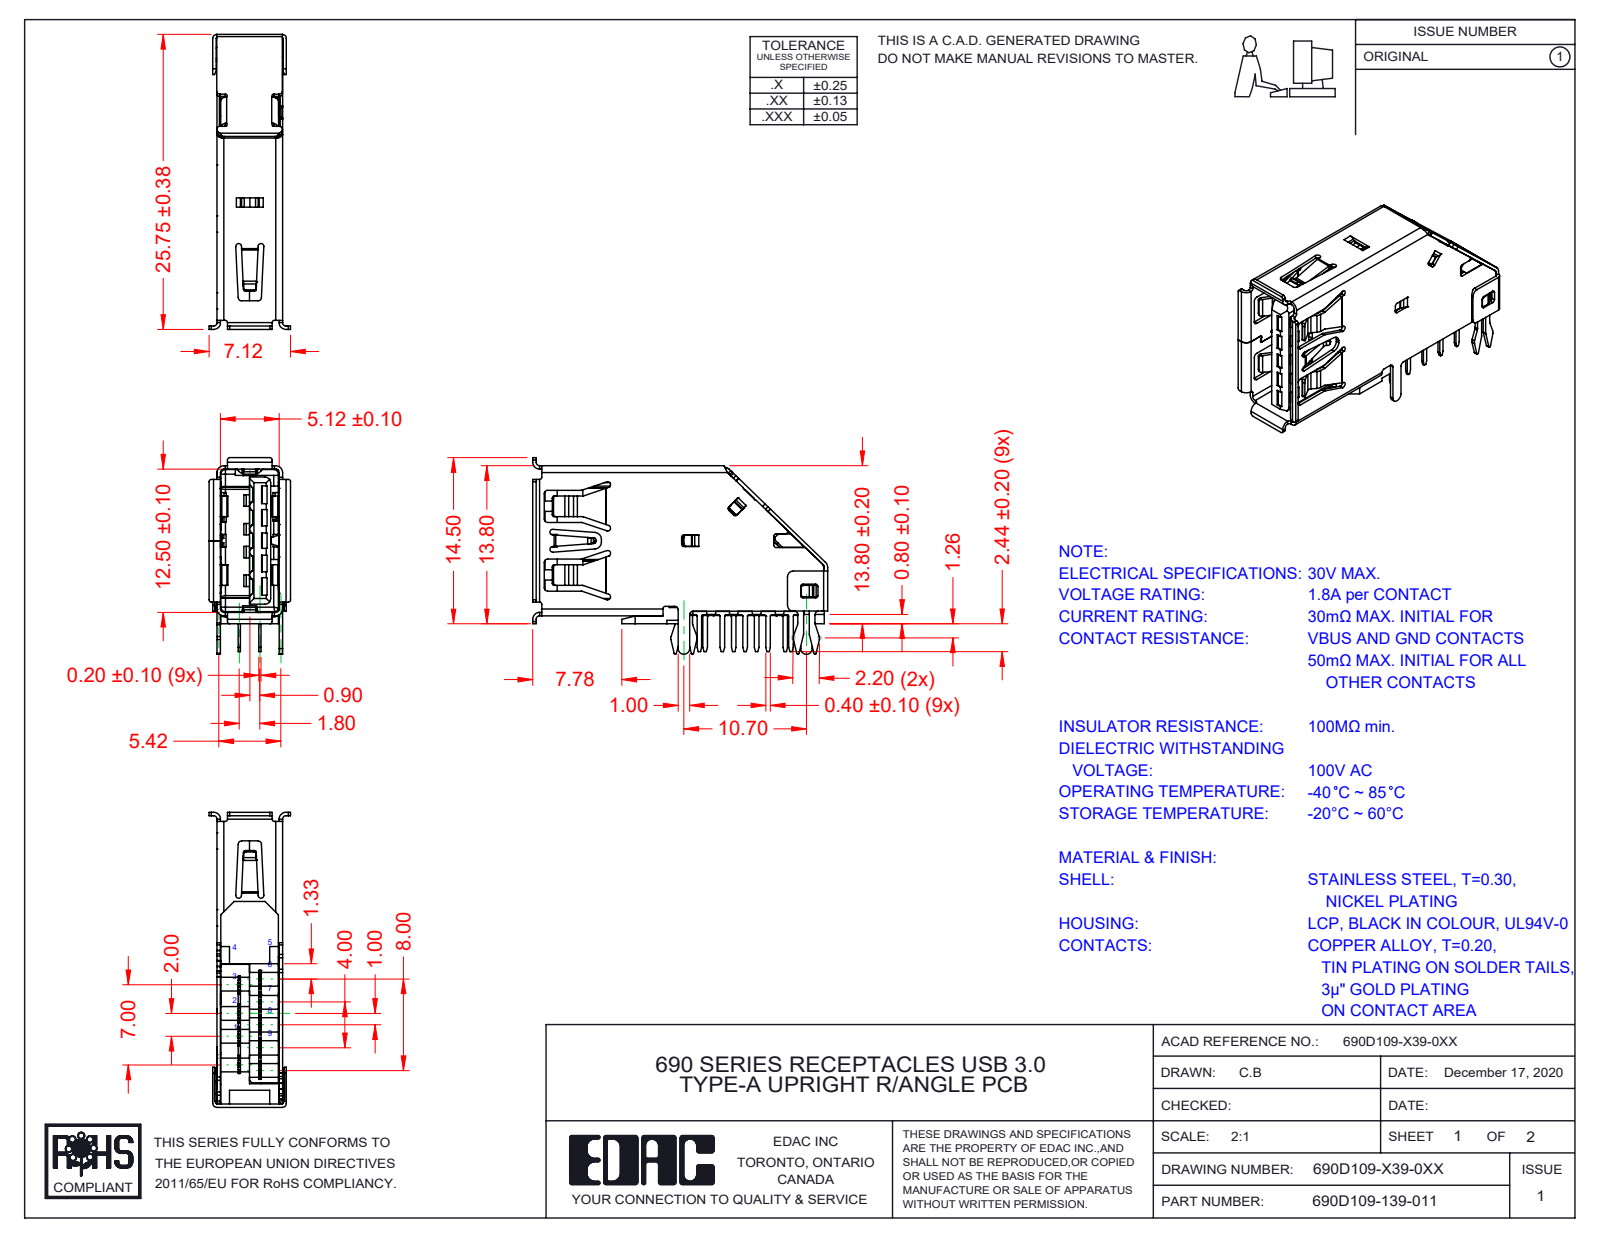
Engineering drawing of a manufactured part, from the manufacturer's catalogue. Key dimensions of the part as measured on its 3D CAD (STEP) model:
Part name (STEP PRODUCT): Contact 2.0 1 690D109-X39-0XX; Contact 3.0 6 690D109-X39-0XX; Contact 2.0 3 690D109-X39-0XX; Shell 2 690D109-X39-0XX (+8 more)
STEP written by: SolidWorks 2020 (AUTOMOTIVE_DESIGN)
Units: millimetres
Bodies: 13 solids, 2780 faces (1938 planar, 770 cylindrical, 72 other)
Overall size (bounding box): 25.75 × 17.16 × 7.12
Volume: 1 030 mm³ · Surface area: 4 329 mm²
Round holes (diameter × count): ⌀0.8 ×1
Partial cylindrical surfaces — rounded edges, fillets, slot ends (radius × count): R0.3 ×78, R0.2 ×76, R0.1 ×66, R0.15 ×43, R0.5 ×36, R0.6 ×30, R0.4 ×24, R0.12 ×18
Main face-to-face distances: 5.42, 2.84, 0.8, 2.54, 2.58, 5.72, 2.88, 5.12, 1, 1.8
